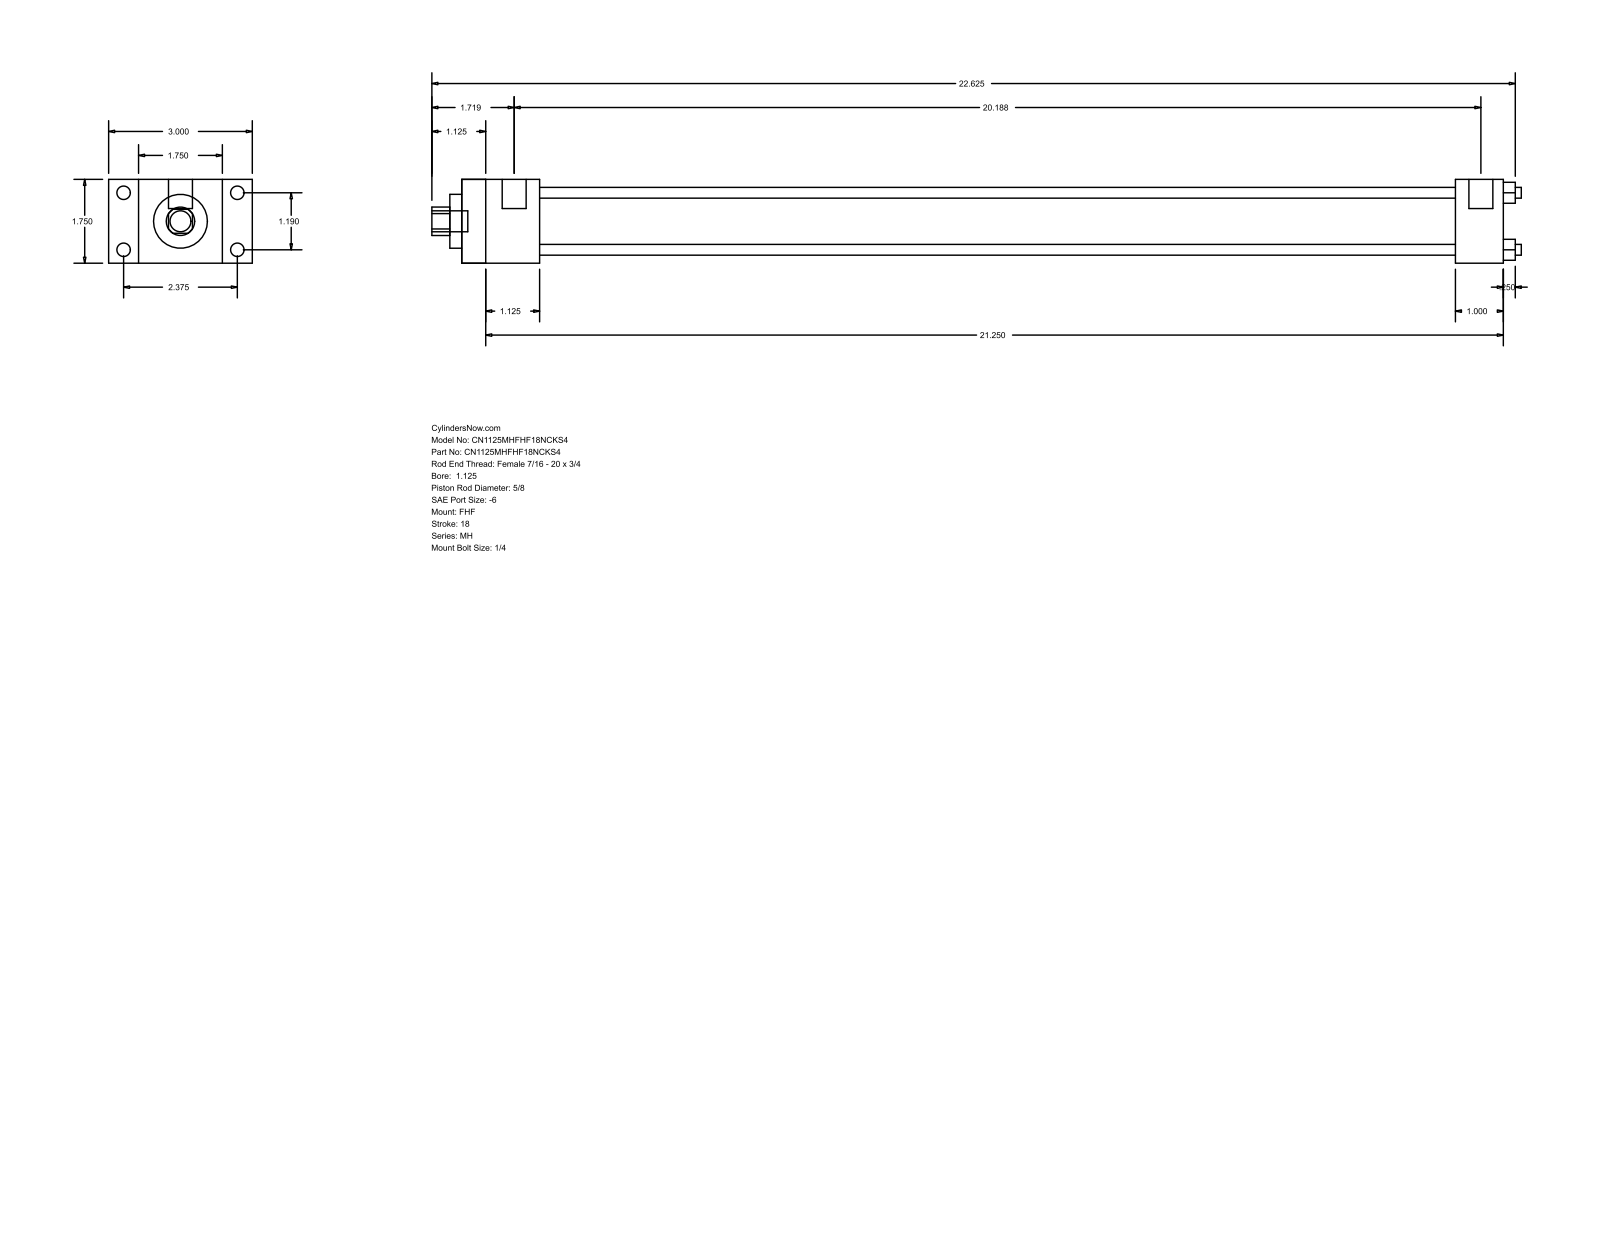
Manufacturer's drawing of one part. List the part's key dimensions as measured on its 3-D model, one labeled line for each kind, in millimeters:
Part name (STEP PRODUCT): MH_FHF__0112_0.625
STEP written by: GSSL Pune (CONFIG_CONTROL_DESIGN)
Units: millimetres
Bodies: 0 solids, 88 faces (60 planar, 28 cylindrical, 0 other)
Overall size (bounding box): 577.85 × 76.2 × 44.45
Round holes (diameter × count): ⌀5.71 ×4, ⌀15.88 ×1, ⌀28.57 ×1, ⌀34.92 ×1
Round bosses / shafts (diameter × count): ⌀7.14 ×4, ⌀5.56 ×4, ⌀12.7 ×2, ⌀11.11 ×1
Partial cylindrical surfaces — rounded edges, fillets, slot ends (radius × count): R7.54 ×1
Main face-to-face distances: 44.46, 15.87, 60.33, 41.27, 76.2, 552.45, 511.18, 527.04, 485.77, 25.41
Hole centre spacings: 21.37, 30.22, 42.74
